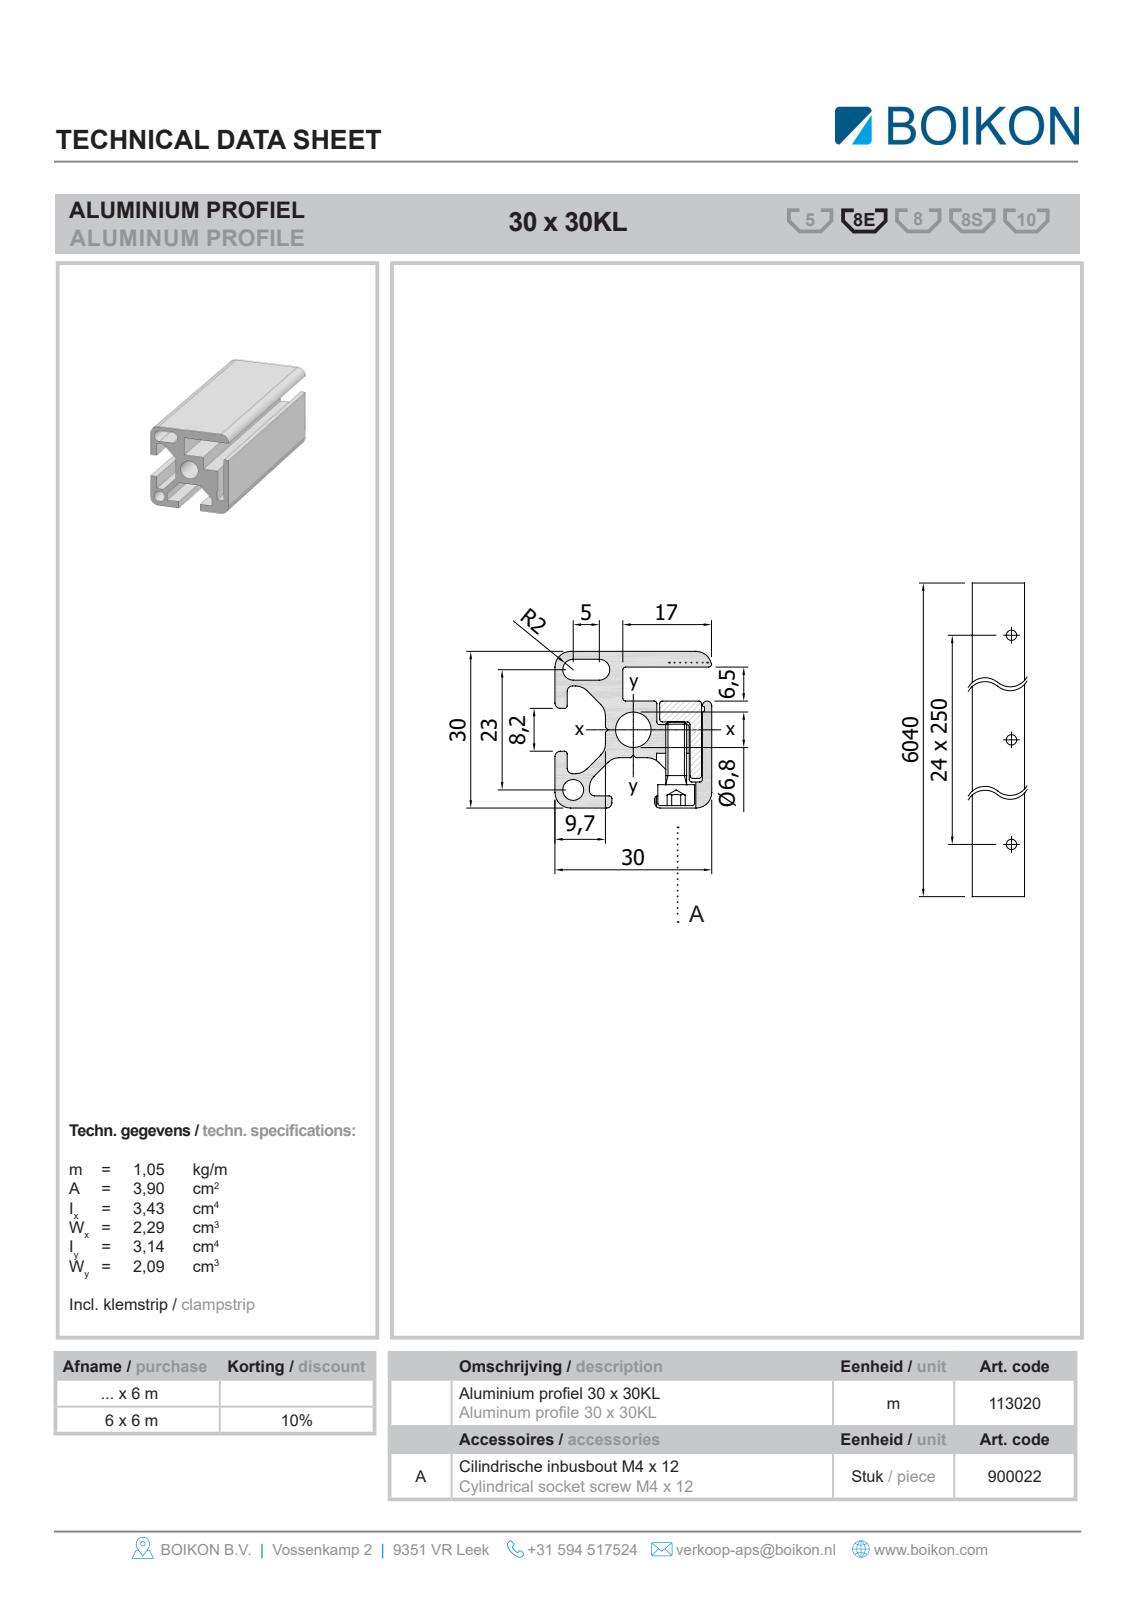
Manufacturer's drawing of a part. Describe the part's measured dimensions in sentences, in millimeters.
The part is named "Root; 11302030x30-KLBOIKON0". Its 3-D file was written by "HiCAD 2013 1802.4 Build 509 (AUTOMOTIVE_DESIGN)". It is 1 solid with 45 faces: 37 planar, 8 cylindrical and 0 other. Overall it measures 1000 by 30 by 30 millimeters. Its volume is 391 242 cubic millimeters and its surface area 300 882 square millimeters. Round holes: 1 of diameter 4, 1 of diameter 6.8. Partial cylindrical surfaces (rounded edges, fillets, slot ends): 4 of radius 3, 2 of radius 2. The main face-to-face distances are 30, 9.7, 20.3, 7.3, 27.6, 2.4, 3, 12.7, 2.5, 27. The hole center spacings are 16.26.
